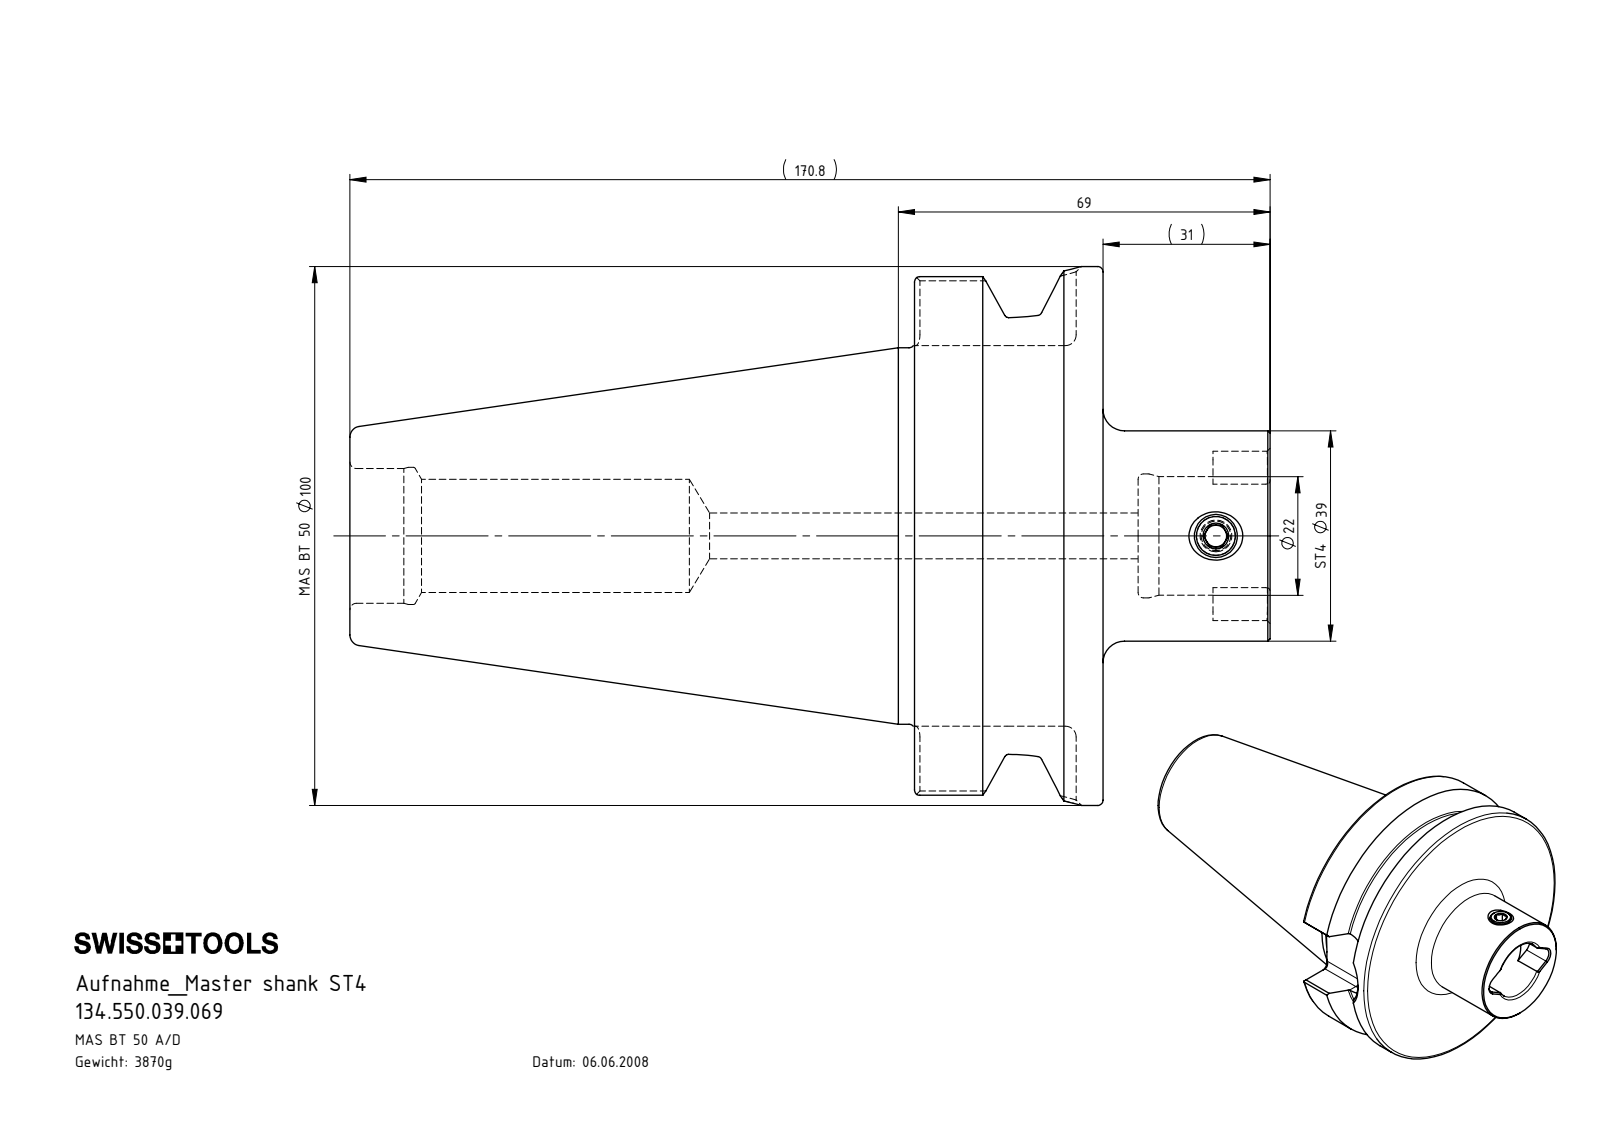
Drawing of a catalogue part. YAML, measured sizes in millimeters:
part_name: "BT5.ST4.K01.069; ST4-ER1.001.011_A; BT5-ST4.K01.069_A"
step_written_by: "SolidWorks 2017 (AUTOMOTIVE_DESIGN)"
units: millimeters
bodies: {solids: 2, faces: 109, planar: 42, cylindrical: 28, other: 39}
overall_size: [170.8, 100, 100]
volume: 492990
surface_area: 56608
round_holes:
  - {diameter: 4, count: 1}
  - {diameter: 7.25, count: 1}
  - {diameter: 8.5, count: 1}
  - {diameter: 21, count: 1}
  - {diameter: 22, count: 1}
  - {diameter: 23, count: 1}
  - {diameter: 25, count: 1}
  - {diameter: 25.45, count: 1}
round_bosses_or_shafts:
  - {diameter: 100, count: 1}
  - {diameter: 85, count: 1}
  - {diameter: 69.85, count: 1}
  - {diameter: 39, count: 1}
  - {diameter: 8, count: 1}
partial_cylinders:
  - {radius: 2, count: 8}
  - {radius: 3.2, count: 2}
  - {radius: 12.85, count: 1}
face_to_face_distances: [35, 66, 31, 70.6, 104.8, 139.8, 170.8, 25.7, 146.3, 41.5]
